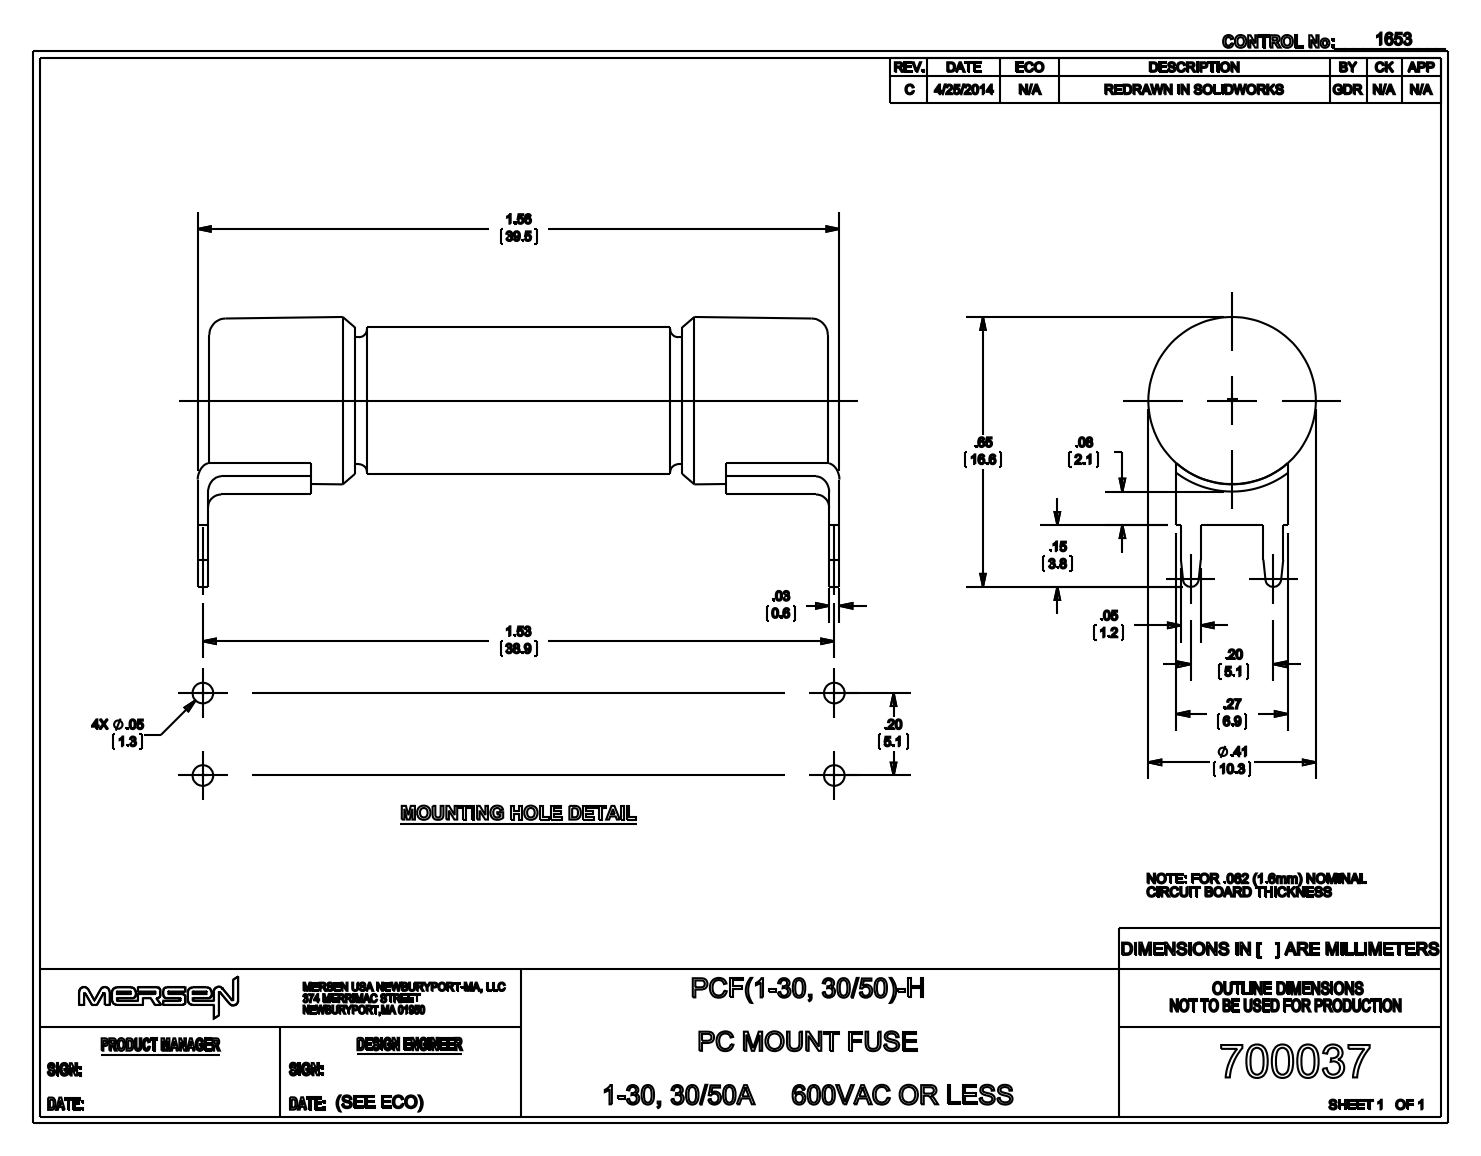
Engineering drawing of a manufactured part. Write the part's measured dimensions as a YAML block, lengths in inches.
part_name: "700037revC"
step_written_by: "SolidWorks 2013 (AUTOMOTIVE_DESIGN)"
units: inches
bodies: {solids: 5, faces: 65, planar: 42, cylindrical: 11, other: 12}
overall_size: [1.556, 0.655, 0.406]
volume: 0.174
surface_area: 2.944
round_bosses_or_shafts:
  - {diameter: 0.356, count: 1}
  - {diameter: 0.308, count: 1}
partial_cylinders:
  - {radius: 0.019, count: 2}
  - {radius: 0.205, count: 1}
  - {radius: 0.23, count: 1}
face_to_face_distances: [0.322, 1.178, 1.5, 1.146, 0.354, 0.824, 0.855, 0.031, 0.353, 0.031]
